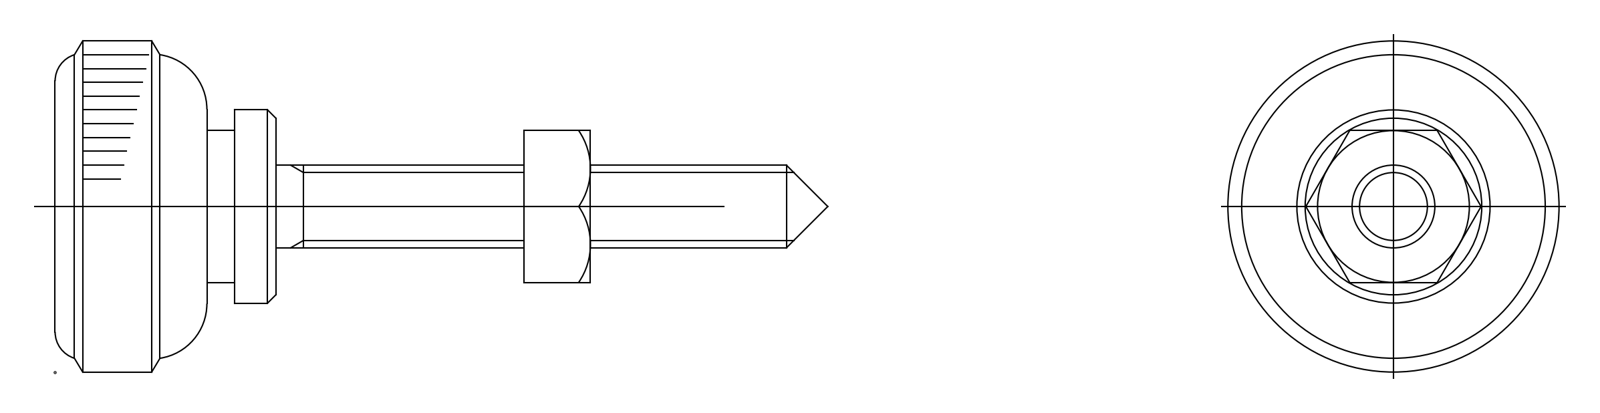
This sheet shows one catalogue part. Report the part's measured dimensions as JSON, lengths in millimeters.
{"part_name": "THA_340SUS_12_3_Nツマミ; M3ナット", "step_written_by": "spGate 20.6.3 (****-****-****-****) (AUTOMOTIVE_DESIGN)", "units": "millimeters", "bodies": {"solids": 2, "faces": 40, "planar": 12, "cylindrical": 10, "other": 18}, "overall_size": [28, 12, 12], "volume_mm3": 802, "surface_area_mm2": 724, "round_holes": [[3, 1]], "round_bosses_or_shafts": [[12, 1], [7, 1], [5.5, 1]], "face_to_face_distances": [5.5, 8, 12.94, 4.94, 15.34, 7.34, 2.4, 2.5, 7.44, 9.84]}
